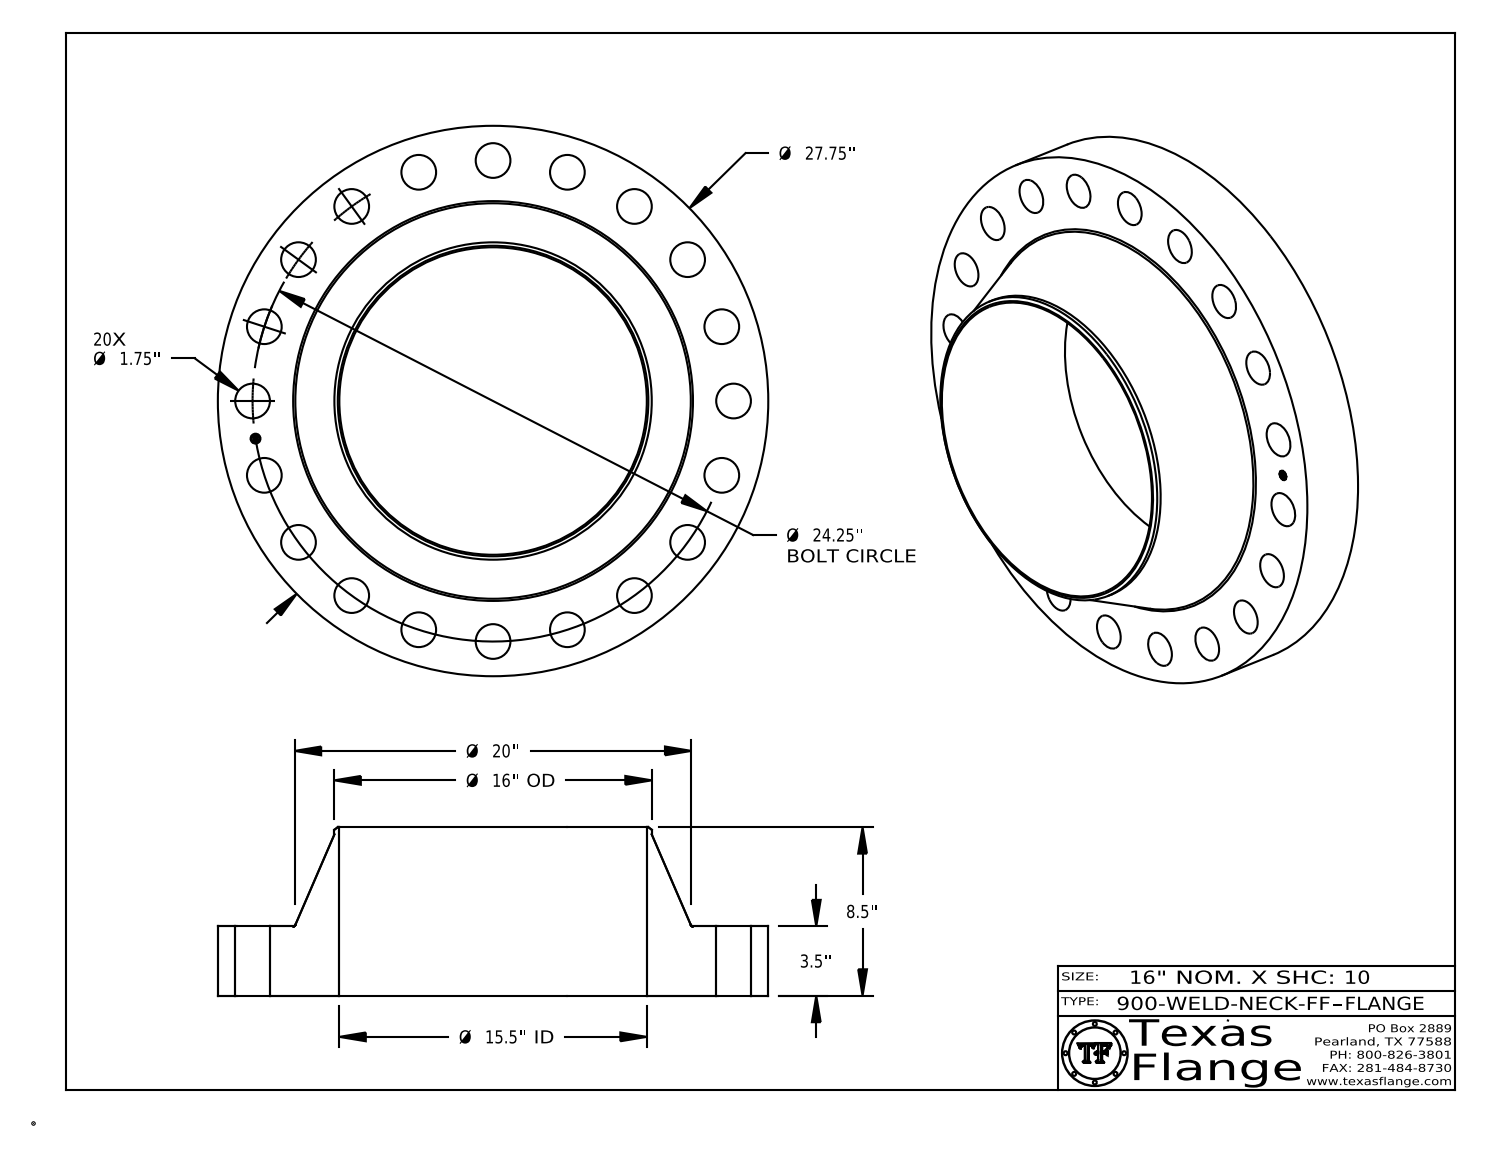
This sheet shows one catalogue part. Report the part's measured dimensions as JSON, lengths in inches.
{"part_name": "900-WELD-NECK-FF", "step_written_by": "CATIA V5 STEP AP214 (AUTOMOTIVE_DESIGN)", "units": "inches", "bodies": {"solids": 1, "faces": 440, "planar": 368, "cylindrical": 66, "other": 6}, "overall_size": [27.75, 27.75, 8.5], "volume_in3": 1602, "surface_area_in2": 2025, "round_holes": [[1.75, 20], [0.495, 1], [15.5, 1]], "round_bosses_or_shafts": [[0.03, 8], [27.75, 1], [16, 1], [0.39, 1]], "face_to_face_distances": [3.5, 8.5, 5, 3.485, 0.015, 5.015, 0.148, 0.145, 0.027, 0.096], "hole_center_spacings": [17.147, 23.063, 19.619, 12.125, 3.794, 7.494, 11.009, 14.254]}
